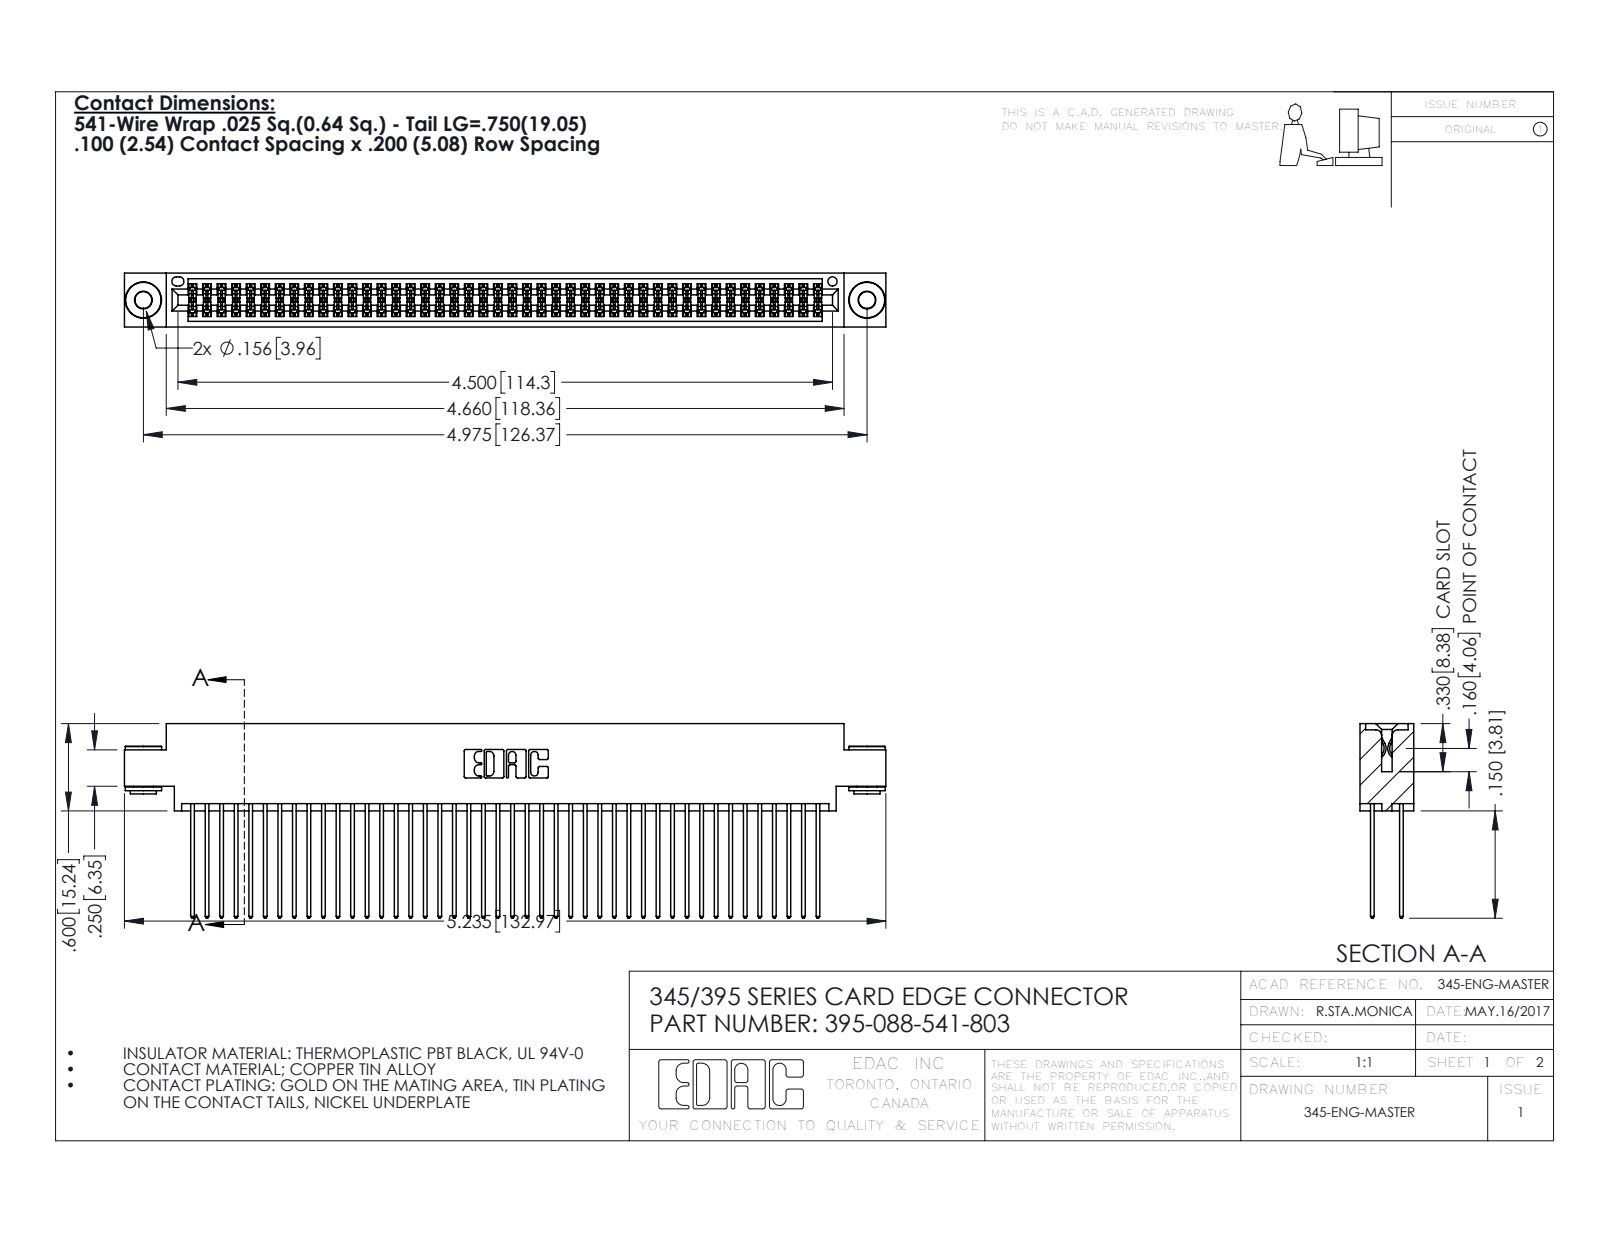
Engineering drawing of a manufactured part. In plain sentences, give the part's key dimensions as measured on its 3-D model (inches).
The part is named "395-088-541-803; 345-250-002_345-250-002-102; 345 Part_0.170 Offset - 0.156 Dia-TH; 345-292-001_345-293-141". Its 3-D file was written by "SolidWorks 2016 (CONFIG_CONTROL_DESIGN)". It is 91 solids with 4568 faces: 2998 planar, 1562 cylindrical and 8 other. Overall it measures 5.235 by 1.337 by 0.37 inches. Its volume is 0.814 cubic inches and its surface area 34.86 square inches. Round holes: 2 of diameter 0.116, 2 of diameter 0.156, 1 of diameter 0.064. Round bosses or shafts: 2 of diameter 0.25, 2 of diameter 0.18, 2 of diameter 0.136. Partial cylindrical surfaces (rounded edges, fillets, slot ends): 132 of radius 0.006, 88 of radius 0.01, 22 of radius 0.01, 6 of radius 0.007, 6 of radius 0.031, 3 of radius 0.026, 2 of radius 0.014, 2 of radius 0.019. The main face-to-face distances are 0.072, 0.298, 0.2, 0.098, 0.272, 0.025, 0.37, 0.225, 0.175, 0.149. The hole center spacings are 0.27, 4.739, 4.975.
